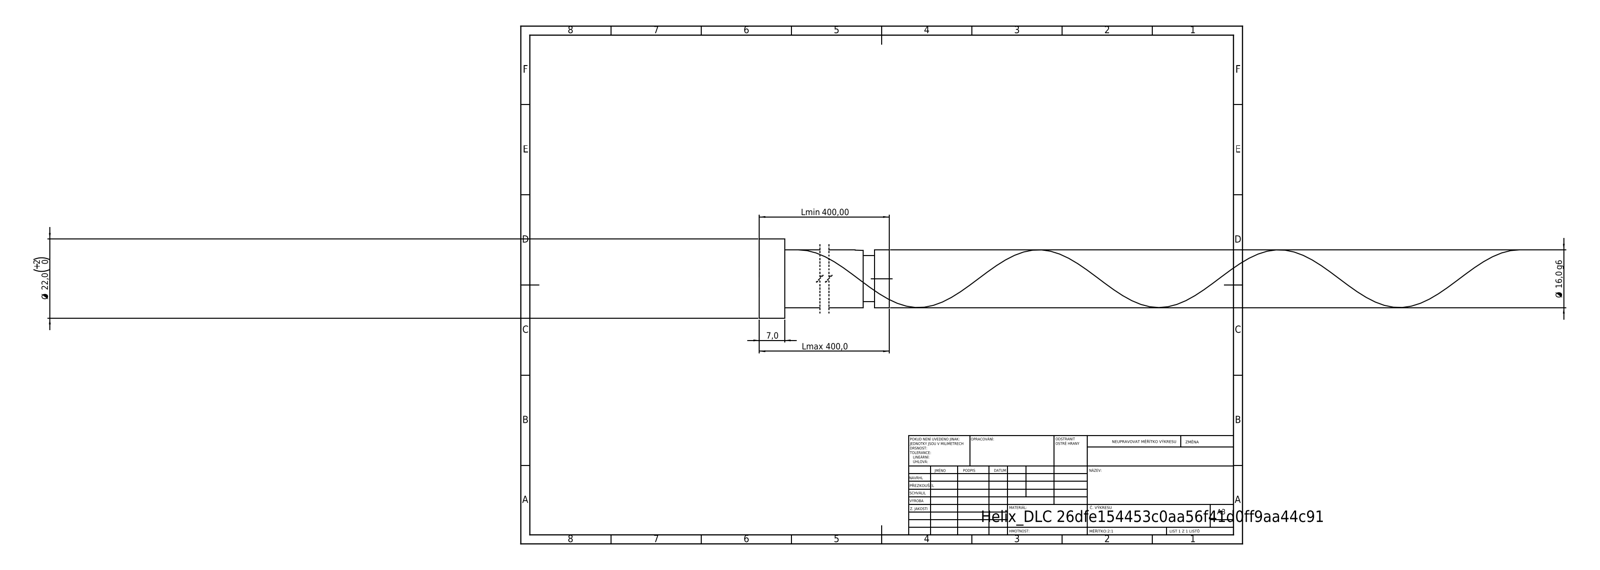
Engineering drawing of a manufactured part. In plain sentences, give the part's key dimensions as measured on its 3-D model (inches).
Its 3-D file was written by "SolidWorks 2019 (CONFIG_CONTROL_DESIGN)". It is 1 solid with 21 faces: 6 planar, 14 cylindrical and 1 other. Overall it measures 15.748 by 0.866 by 0.866 inches. Its volume is 4.923 cubic inches and its surface area 33.36 square inches. Round bosses or shafts: 1 of diameter 0.866, 1 of diameter 0.63, 1 of diameter 0.504. The main face-to-face distances are 15.748, 0.276, 15.472, 15.589, 15.313, 0.159, 15.463, 15.187, 0.126, 0.285.
